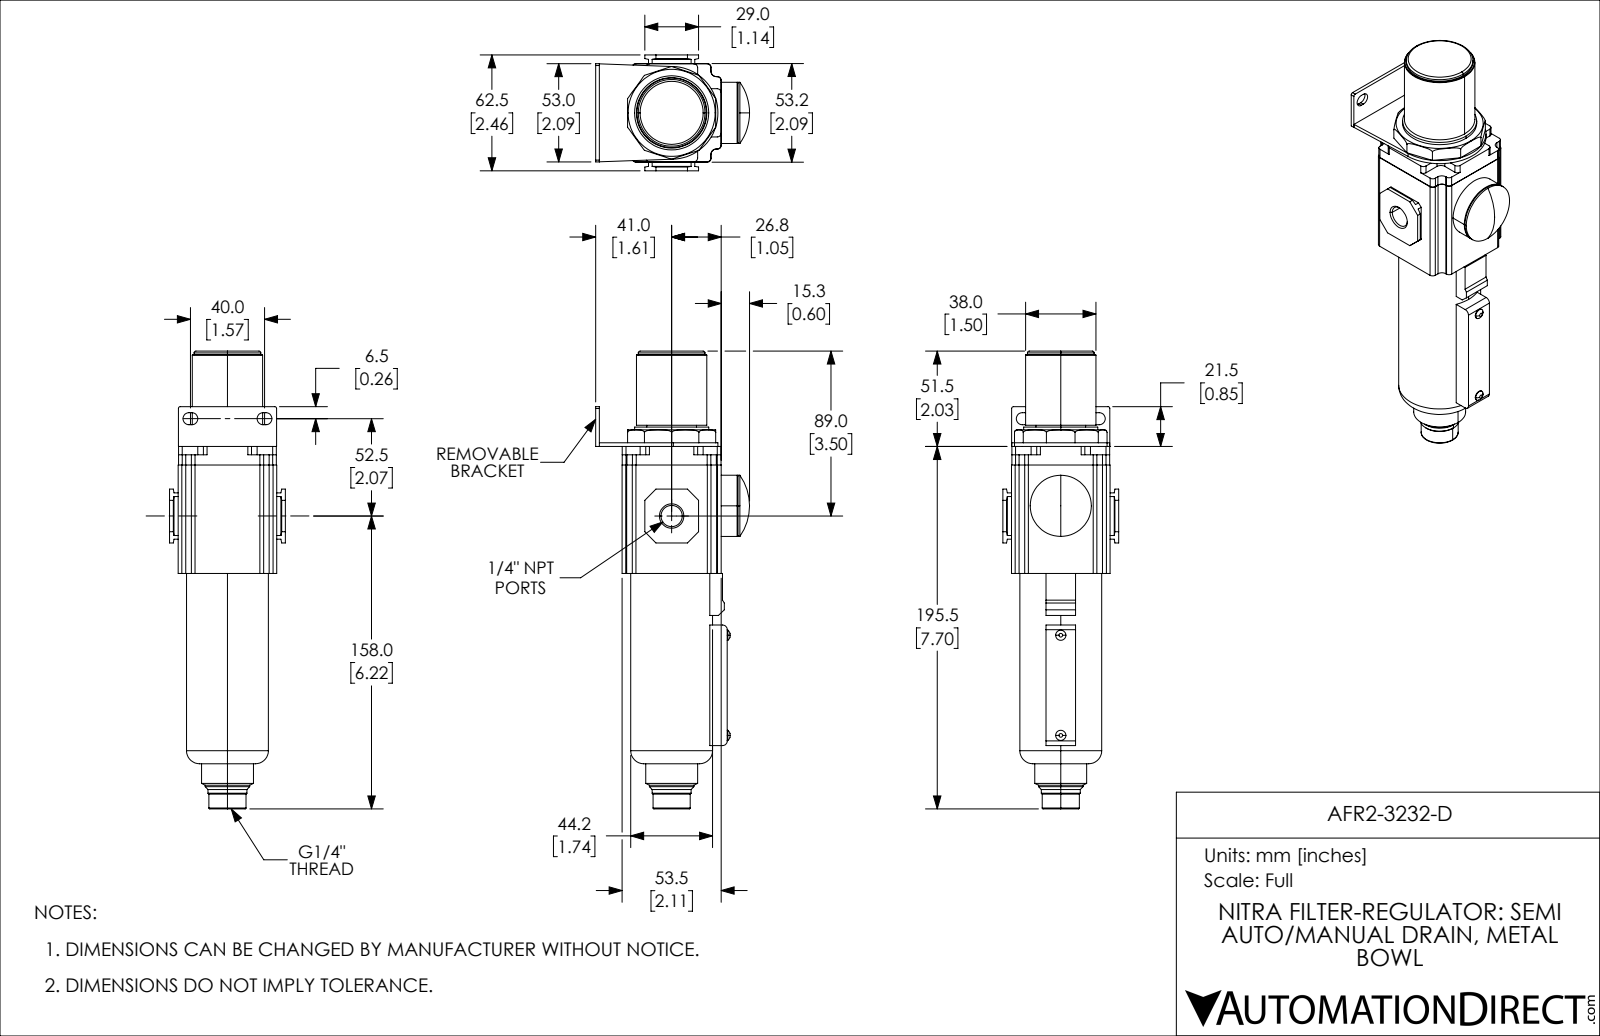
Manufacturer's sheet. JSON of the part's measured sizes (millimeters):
{"part_name": "AFR2-3232-D", "step_written_by": "SolidWorks 2019 (CONFIG_CONTROL_DESIGN)", "units": "millimeters", "bodies": {"solids": 1, "faces": 235, "planar": 128, "cylindrical": 77, "other": 30}, "overall_size": [247, 83.03, 62.5], "volume_mm3": 442048, "surface_area_mm2": 52289, "round_holes": [[11.45, 2]], "round_bosses_or_shafts": [[5.5, 2], [44.2, 1], [40, 1], [38, 1], [36, 1], [33, 1], [28, 1], [26.78, 1]], "partial_cylinders_radius": [[2, 24], [3, 12], [3.25, 4], [1, 2], [2.5, 2], [25, 1]], "face_to_face_distances": [2, 53.2, 18.6, 34.6, 39.25, 16, 53.5, 4.65, 23.25, 57.85]}
